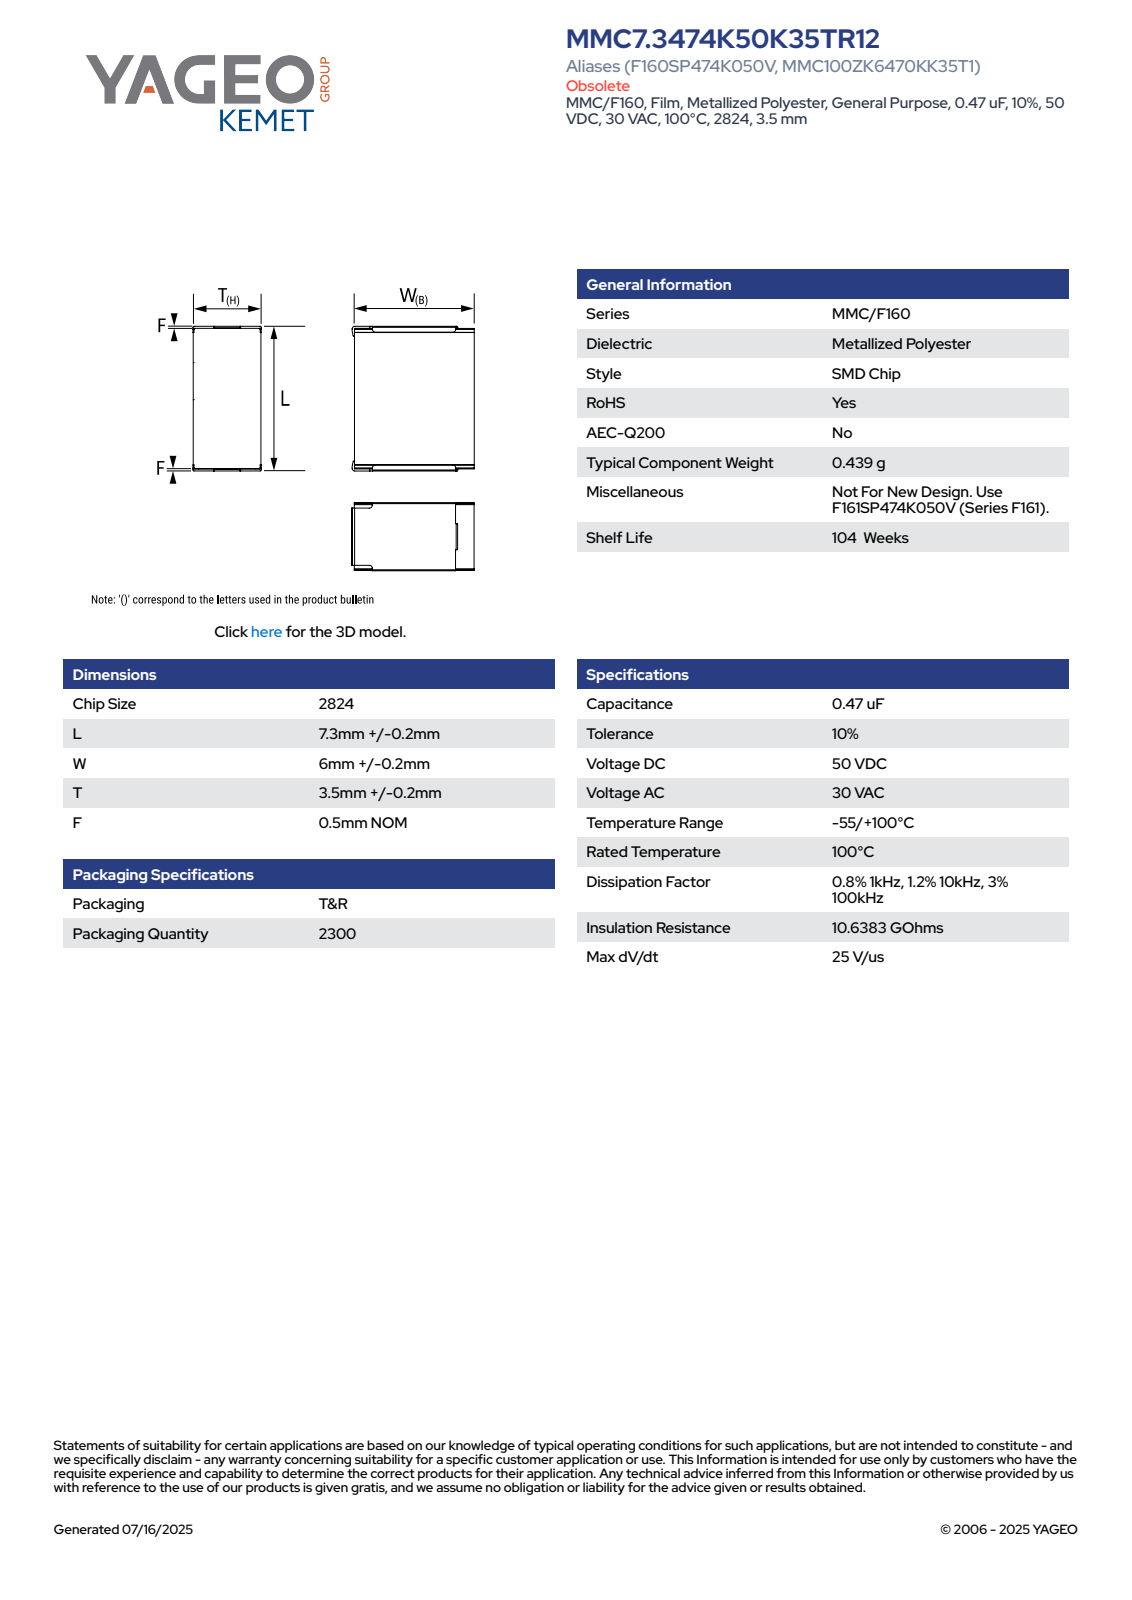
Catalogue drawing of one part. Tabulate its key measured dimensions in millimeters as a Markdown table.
| quantity | value |
| --- | --- |
| part name | CFS_KSTD_2824_L7.50W6.20T3.7F0.5 |
| STEP written by | SolidWorks 2021 (AUTOMOTIVE_DESIGN) |
| units | millimeters |
| bodies | 4 solids, 117 faces (103 planar, 14 cylindrical, 0 other) |
| overall size | 7.5 × 6.41 × 3.89 |
| volume | 164 mm³ |
| surface area | 203 mm² |
| partial cylindrical surfaces (radius × count) | 0.22 × 10, 0.26 × 4 |
| main face-to-face distances | 3.7, 5.95, 7.5, 0.5, 7, 3.79, 6.5, 3.88, 6.41, 0.46 |
